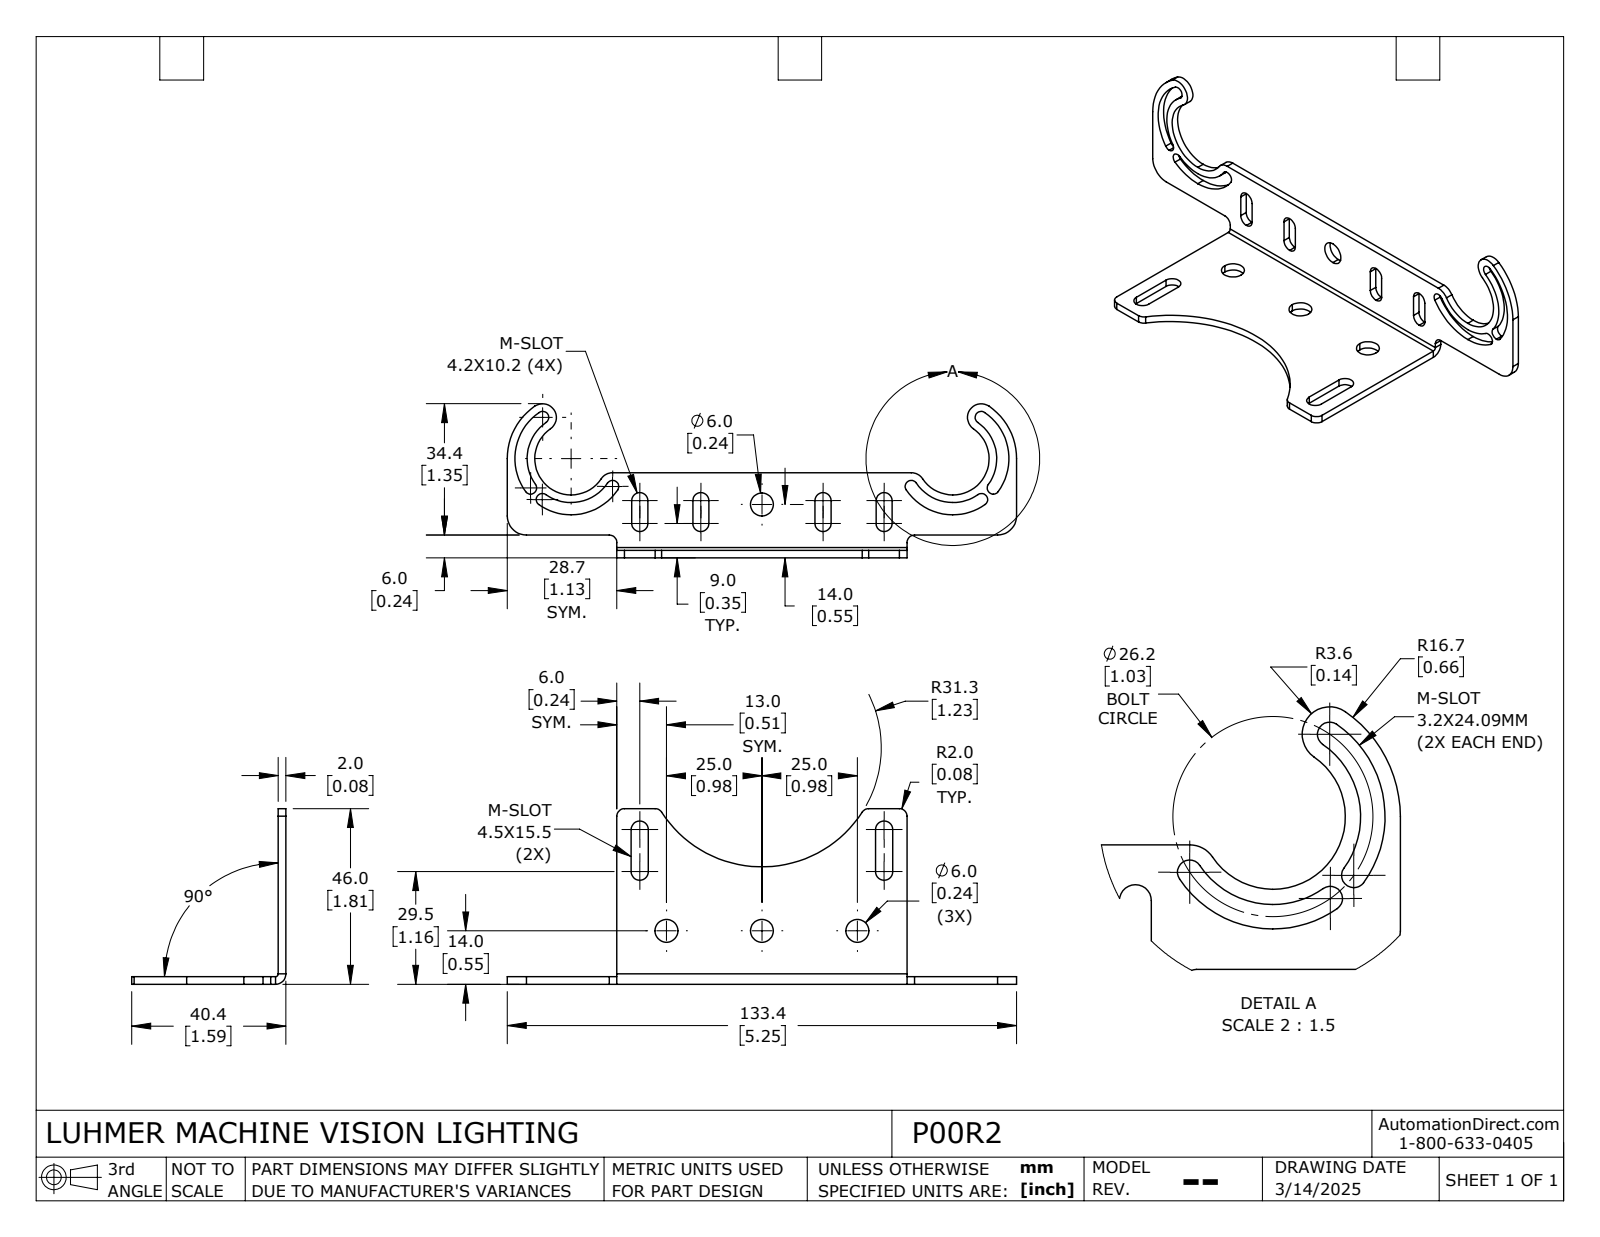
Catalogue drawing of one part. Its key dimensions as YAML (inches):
part_name: "P00R2"
step_written_by: "SolidWorks 2024 (AUTOMOTIVE_DESIGN)"
units: inches
bodies: {solids: 1, faces: 96, planar: 29, cylindrical: 67, other: 0}
overall_size: [5.252, 1.811, 1.59]
volume: 0.581
surface_area: 17.66
round_holes:
  - {diameter: 0.236, count: 4}
partial_cylinders:
  - {radius: 0.063, count: 8}
  - {radius: 0.083, count: 8}
  - {radius: 0.079, count: 6}
  - {radius: 0.089, count: 4}
  - {radius: 0.142, count: 4}
  - {radius: 0.197, count: 2}
  - {radius: 0.374, count: 2}
  - {radius: 0.453, count: 2}
face_to_face_distances: [0.079, 0.8, 0.879, 2.992, 0.643, 0.157, 0.236, 2.52, 1.13, 4.122]
hole_center_spacings: [0.984, 1.969]
